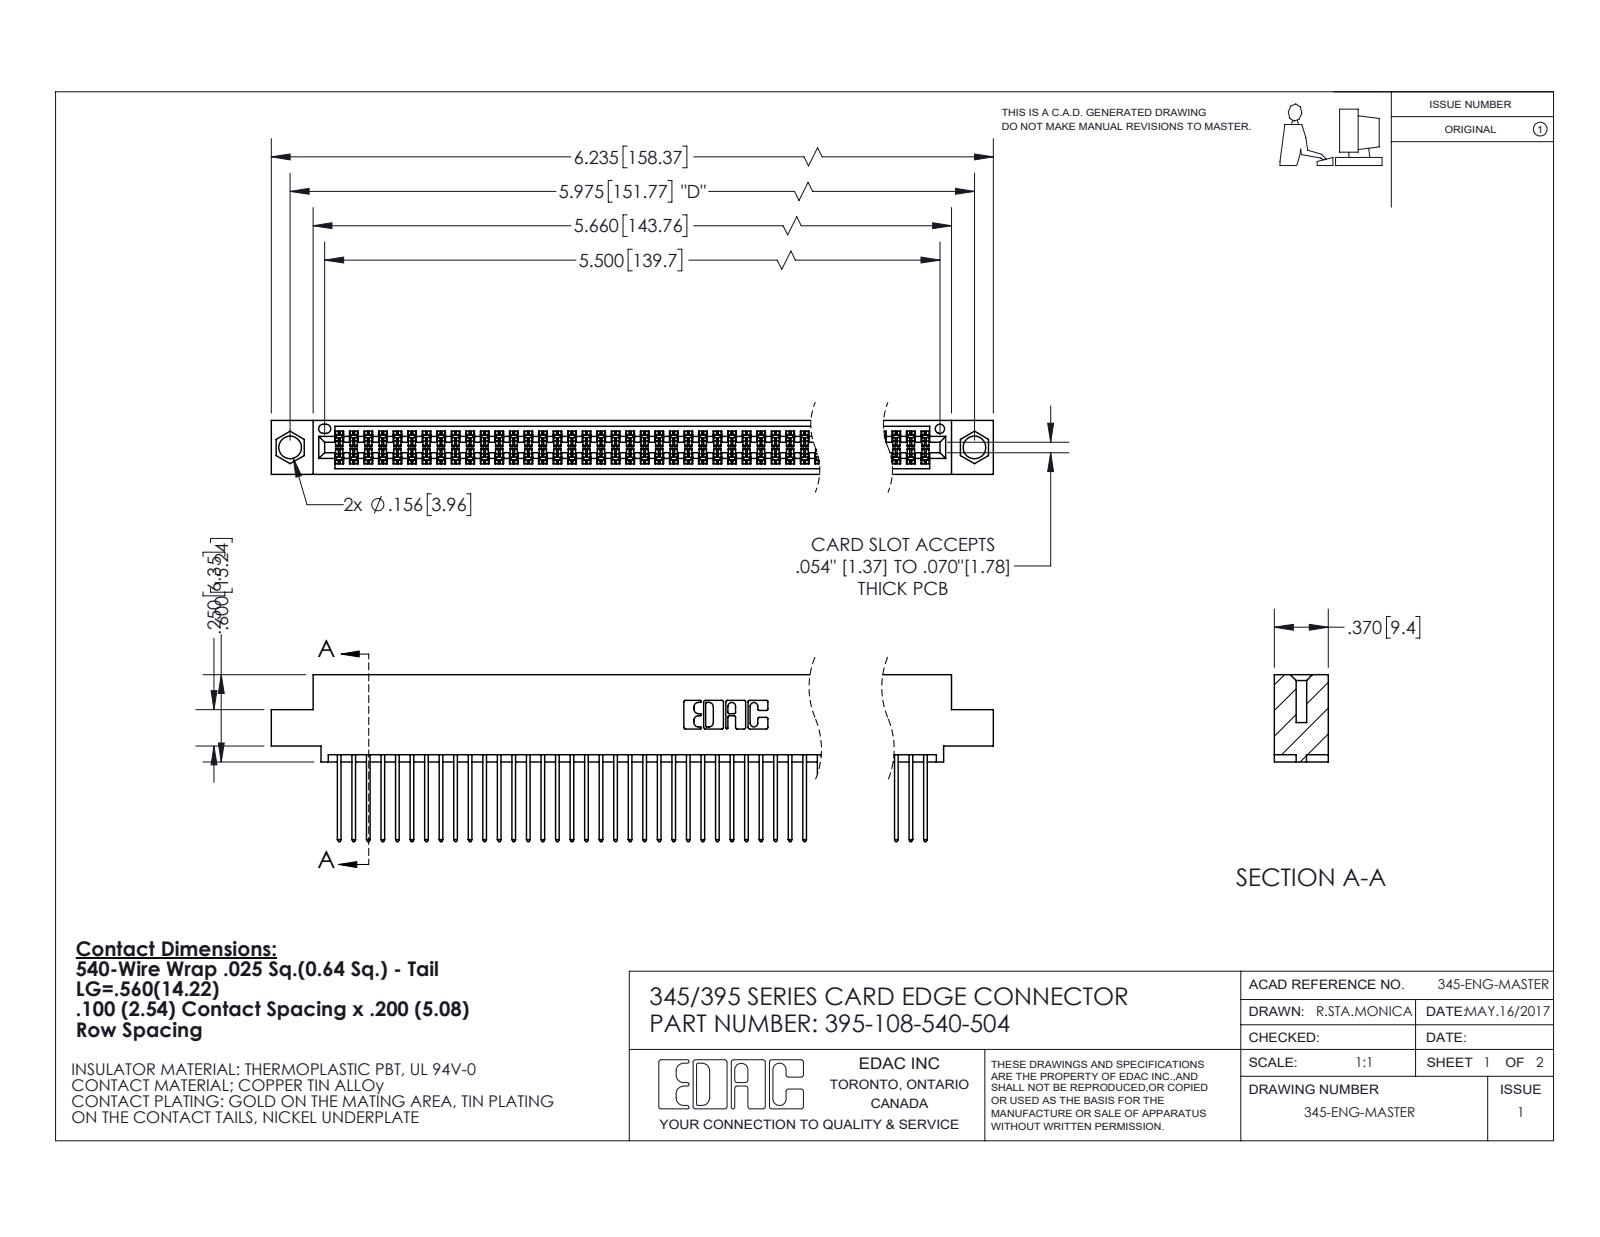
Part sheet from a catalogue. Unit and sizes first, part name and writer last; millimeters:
Units: millimetres
Overall size (bounding box): 158.4 × 29.1 × 9.4
Round holes (diameter × count): ⌀4 ×2, ⌀1.6 ×1
Partial cylindrical surfaces — rounded edges, fillets, slot ends (radius × count): R0.2 ×216, R0.3 ×108, R0.3 ×22, R0.2 ×6, R0.8 ×6, R0.7 ×3, R0.4 ×2, R0.5 ×2
Main face-to-face distances: 7.6, 1.8, 5.1, 2.5, 6.9, 0.6, 9.4, 5.7, 4.4, 3.8
Hole centre spacings: 6.9, 145.8, 151.8
Volume: 15 700 mm³ · Surface area: 25 320 mm²
Bodies: 109 solids, 5544 faces (3662 planar, 1882 cylindrical, 0 other)
Part name (STEP PRODUCT): 345-292-001_345-293-140; 395-108-540-504; 345 Part_0.110 Offset - 0.156 Dia-TI
STEP written by: SolidWorks 2020 (CONFIG_CONTROL_DESIGN)
